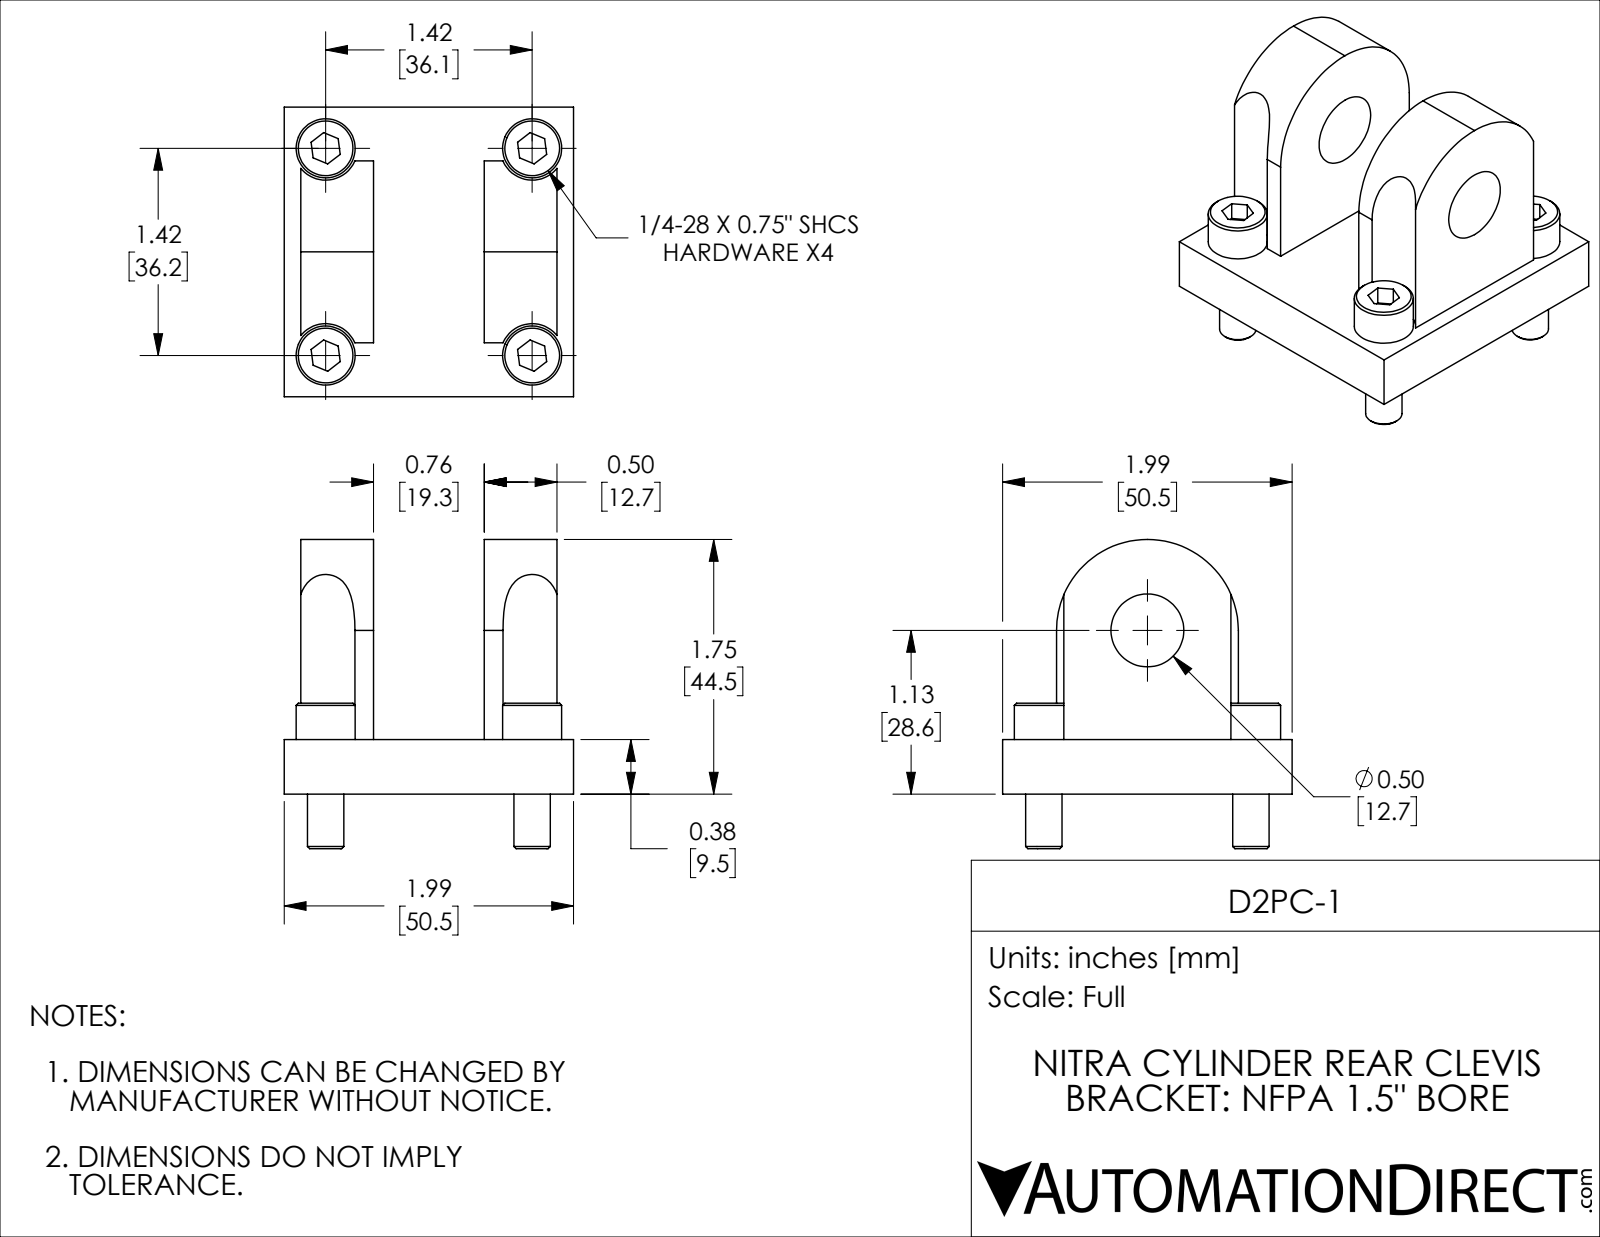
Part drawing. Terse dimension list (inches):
name: D2PC-1
written by: SolidWorks 2019 (CONFIG_CONTROL_DESIGN)
unit: in
bodies: 5 solids, 106 faces (54 planar, 36 cylindrical, 16 other)
size: 2.125 × 1.99 × 1.99
volume: 2.858 in³; area: 26.1 in²
holes: 4× ⌀0.281, 1× ⌀0.501
bosses: 4× ⌀0.406, 4× ⌀0.25
rounds: 4× R0.219, 1× R0.625
face distances: 0.375, 0.5, 1.26, 0.115, 0.615, 1.375, 1.875, 1.99, 0.76, 1.76
hole spacings: 1.42, 1.424, 2.011
